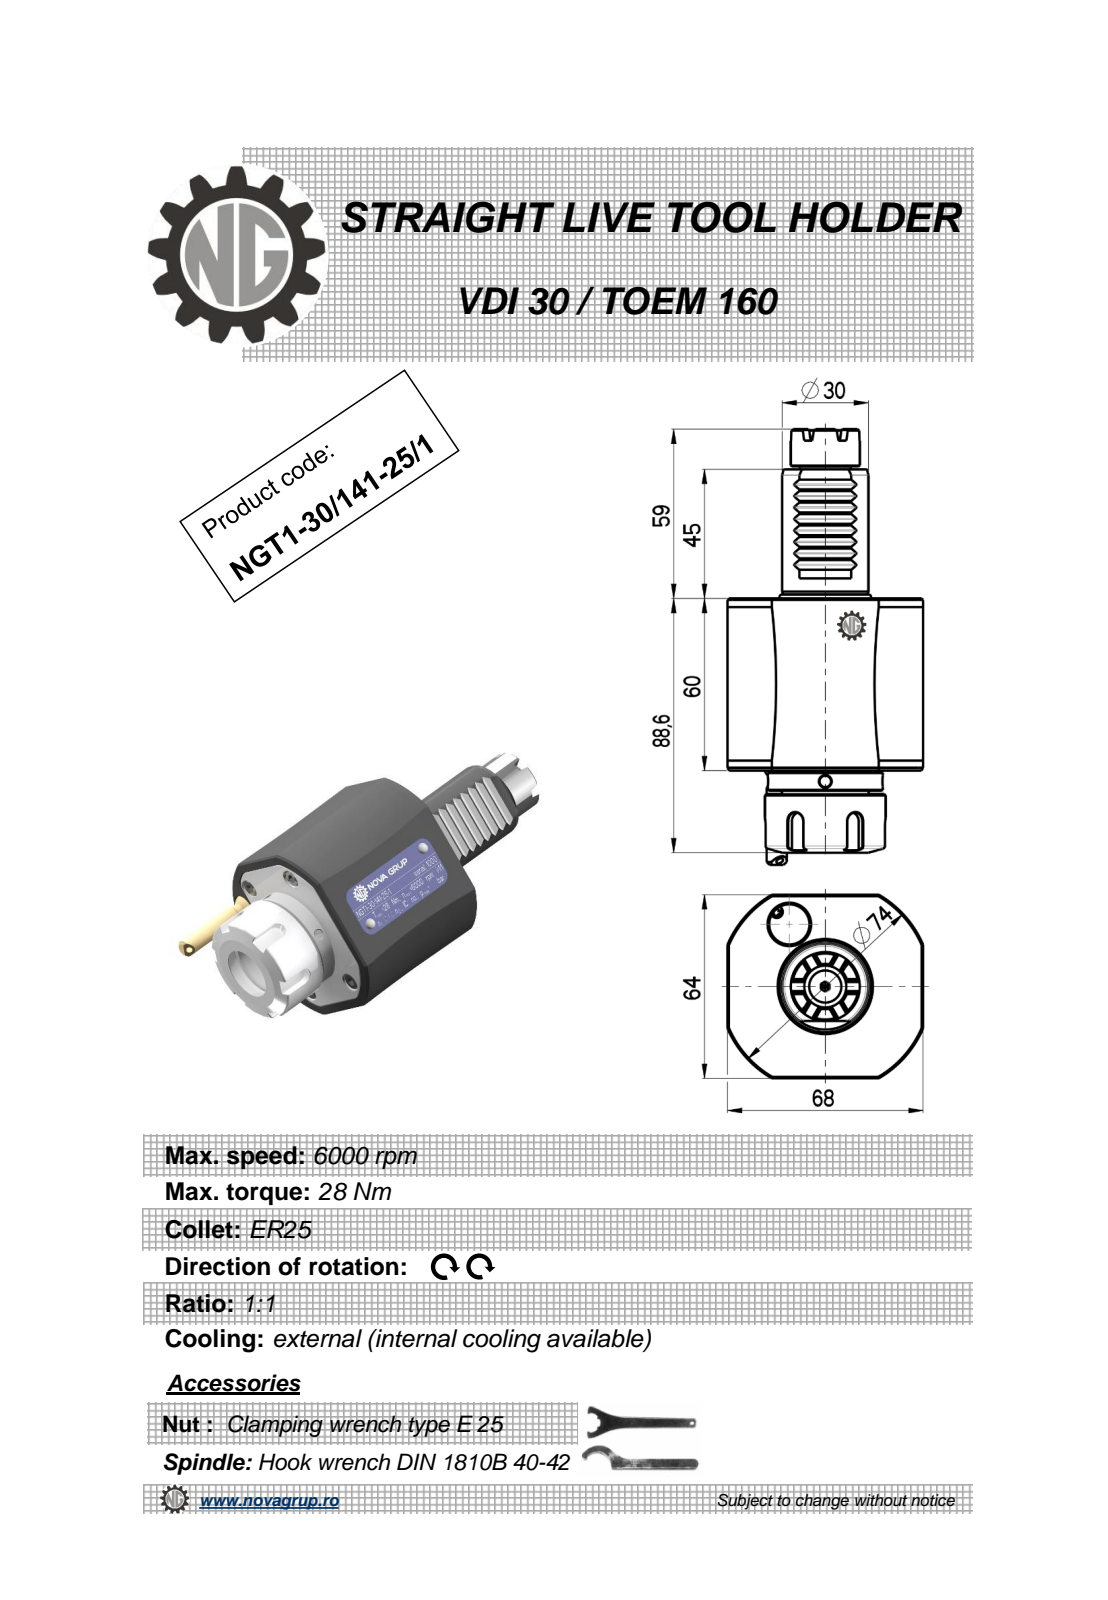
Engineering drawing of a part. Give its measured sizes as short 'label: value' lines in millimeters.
name: NGT1_30_141_25_1
written by: PRO/ENGINEER BY PARAMETRIC TECHNOLOGY CORPORATION, 2010280 (CONFIG_CONTROL_DESIGN)
unit: mm
bodies: 1 solid, 291 faces (123 planar, 63 cylindrical, 105 other)
size: 151.83 × 68 × 65.6
volume: 303 866 mm³; area: 34 700 mm²
holes: 2× ⌀4, 1× ⌀2.5, 1× ⌀3, 1× ⌀20.3
bosses: 1× ⌀42, 1× ⌀40, 1× ⌀33, 1× ⌀30, 1× ⌀24, 1× ⌀17.7, 1× ⌀15.2, 1× ⌀9
rounds: 8× R0.3, 5× R3, 1× R37
face distances: 60, 64, 68, 83.7, 23.7, 2.83, 68.1, 8.1, 15.6, 7
hole spacings: 31
